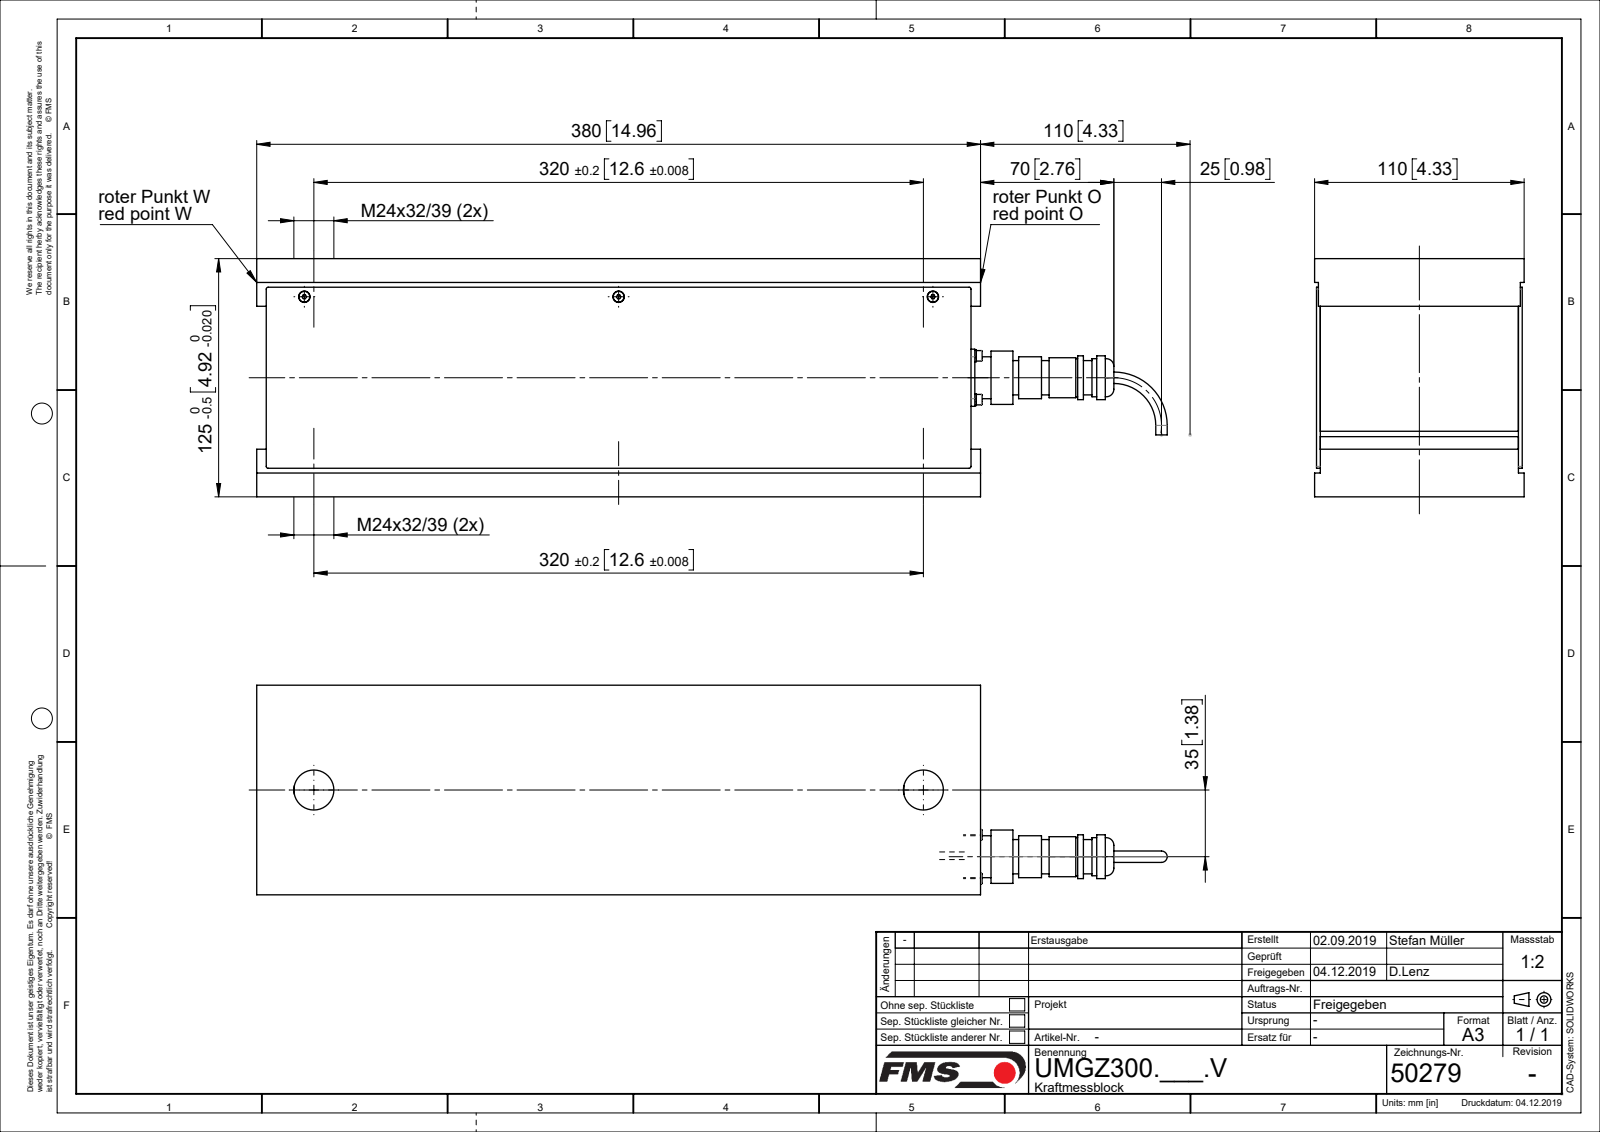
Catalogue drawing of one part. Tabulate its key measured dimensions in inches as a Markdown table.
| quantity | value |
| --- | --- |
| part name | U50279; U4997504; U49976; TEIL1 (+5 more) |
| STEP written by | Mechanical Desktop 2007 (CONFIG_CONTROL_DESIGN) |
| units | inches |
| bodies | 18 solids, 375 faces (133 planar, 156 cylindrical, 86 other) |
| overall size | 18.819 × 4.921 × 4.331 |
| volume | 307.3 in³ |
| surface area | 587.3 in² |
| round holes (diameter × count) | 0.102 × 7, 0.126 × 4, 0.142 × 3, 0.236 × 3, 0.837 × 2 |
| round bosses / shafts (diameter × count) | 0.118 × 7, 0.244 × 4, 0.217 × 4, 0.098 × 4, 1.102 × 1, 0.906 × 1, 0.866 × 1, 0.827 × 1 |
| partial cylindrical surfaces (radius × count) | 0.157 × 4 |
| main face-to-face distances | 0.079, 4.252, 0.118, 4.134, 0.039, 4.213, 4.331, 4.921, 4.173, 4.094 |
| hole center spacings | 0.906, 1.281, 6.496, 12.598, 12.992 |
